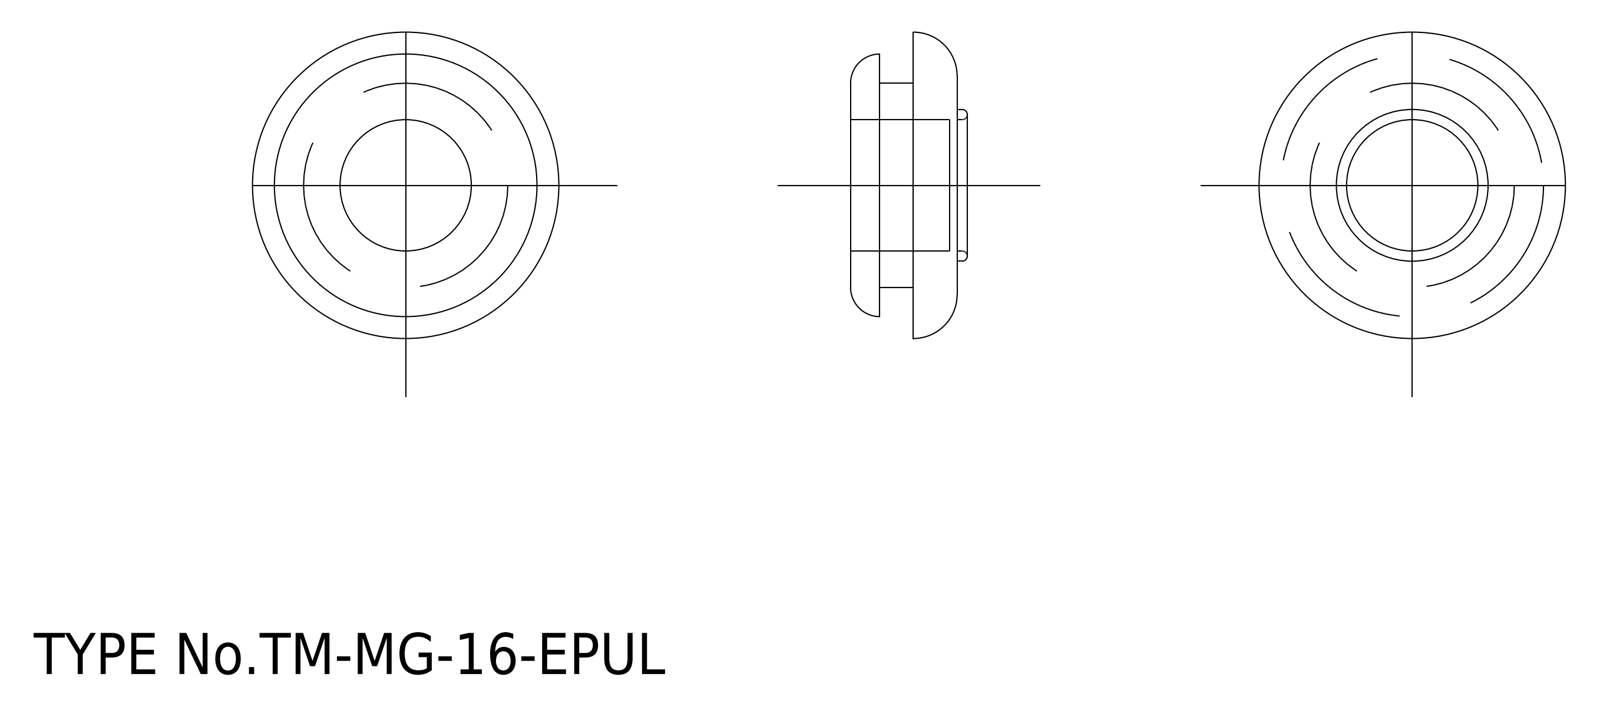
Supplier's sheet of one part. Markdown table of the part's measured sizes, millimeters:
| quantity | value |
| --- | --- |
| STEP written by | spGate 15.6.1 (AUTOMOTIVE_DESIGN) |
| units | millimeters |
| bodies | 1 solid, 20 faces (6 planar, 8 cylindrical, 6 other) |
| overall size | 21 × 21 × 8 |
| volume | 1 317 mm³ |
| surface area | 1 392 mm² |
| round holes (diameter × count) | 9 × 1 |
| round bosses / shafts (diameter × count) | 14 × 1, 10.4 × 1 |
| main face-to-face distances | 3, 2.3, 5.3, 2, 4.3, 7.3, 6.8, 4.8, 2.5, 0.5 |
